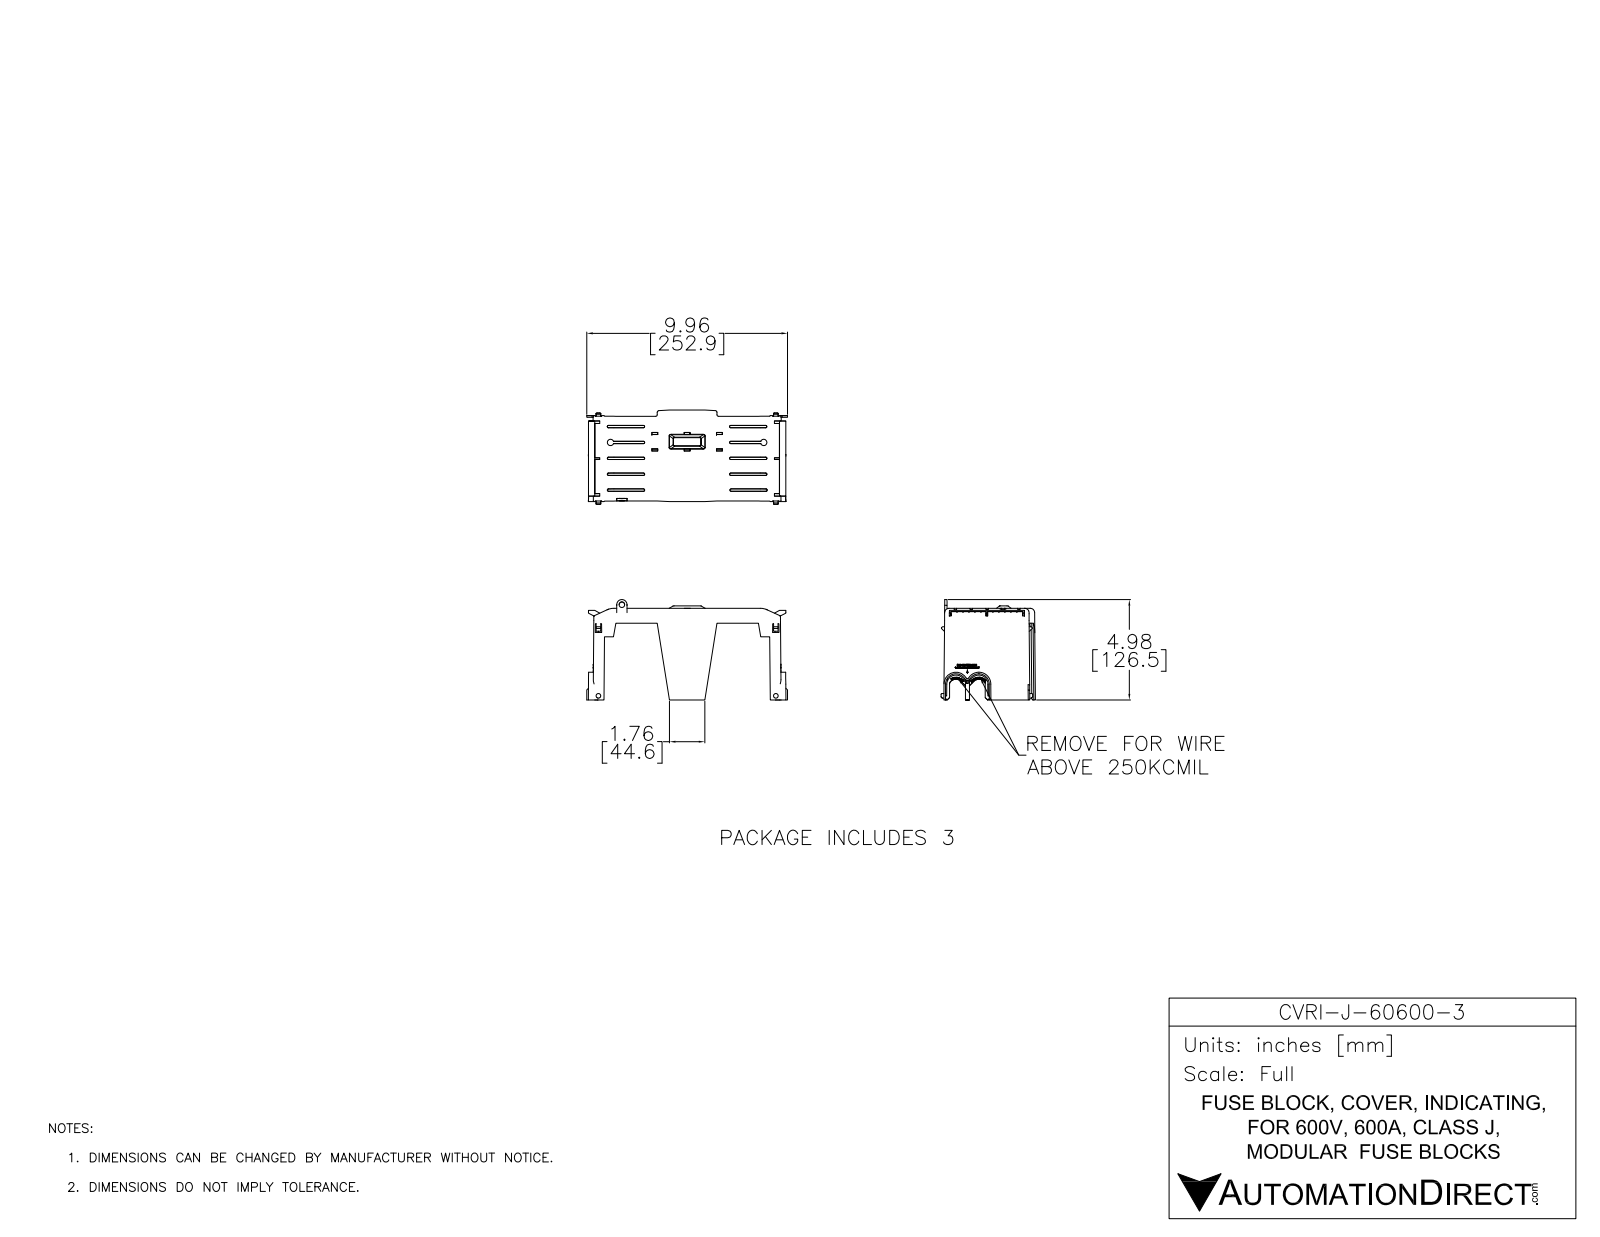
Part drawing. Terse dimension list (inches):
name: CVRI-J-60600-3
written by: SolidWorks 2017 (AUTOMOTIVE_DESIGN)
unit: in
bodies: 1 solid, 2344 faces (1597 planar, 167 cylindrical, 580 other)
size: 9.959 × 4.983 × 4.677
volume: 10.27 in³; area: 271.3 in²
holes: 1× ⌀0.276
rounds: 18× R0.039, 12× R0.118, 10× R0.028, 9× R0.217, 7× R0.138, 6× R0.079, 4× R0.354, 4× R0.512
face distances: 0.079, 0.079, 0.276, 0.197, 0.354, 0.803, 0.795, 0.118, 1.614, 0.158
